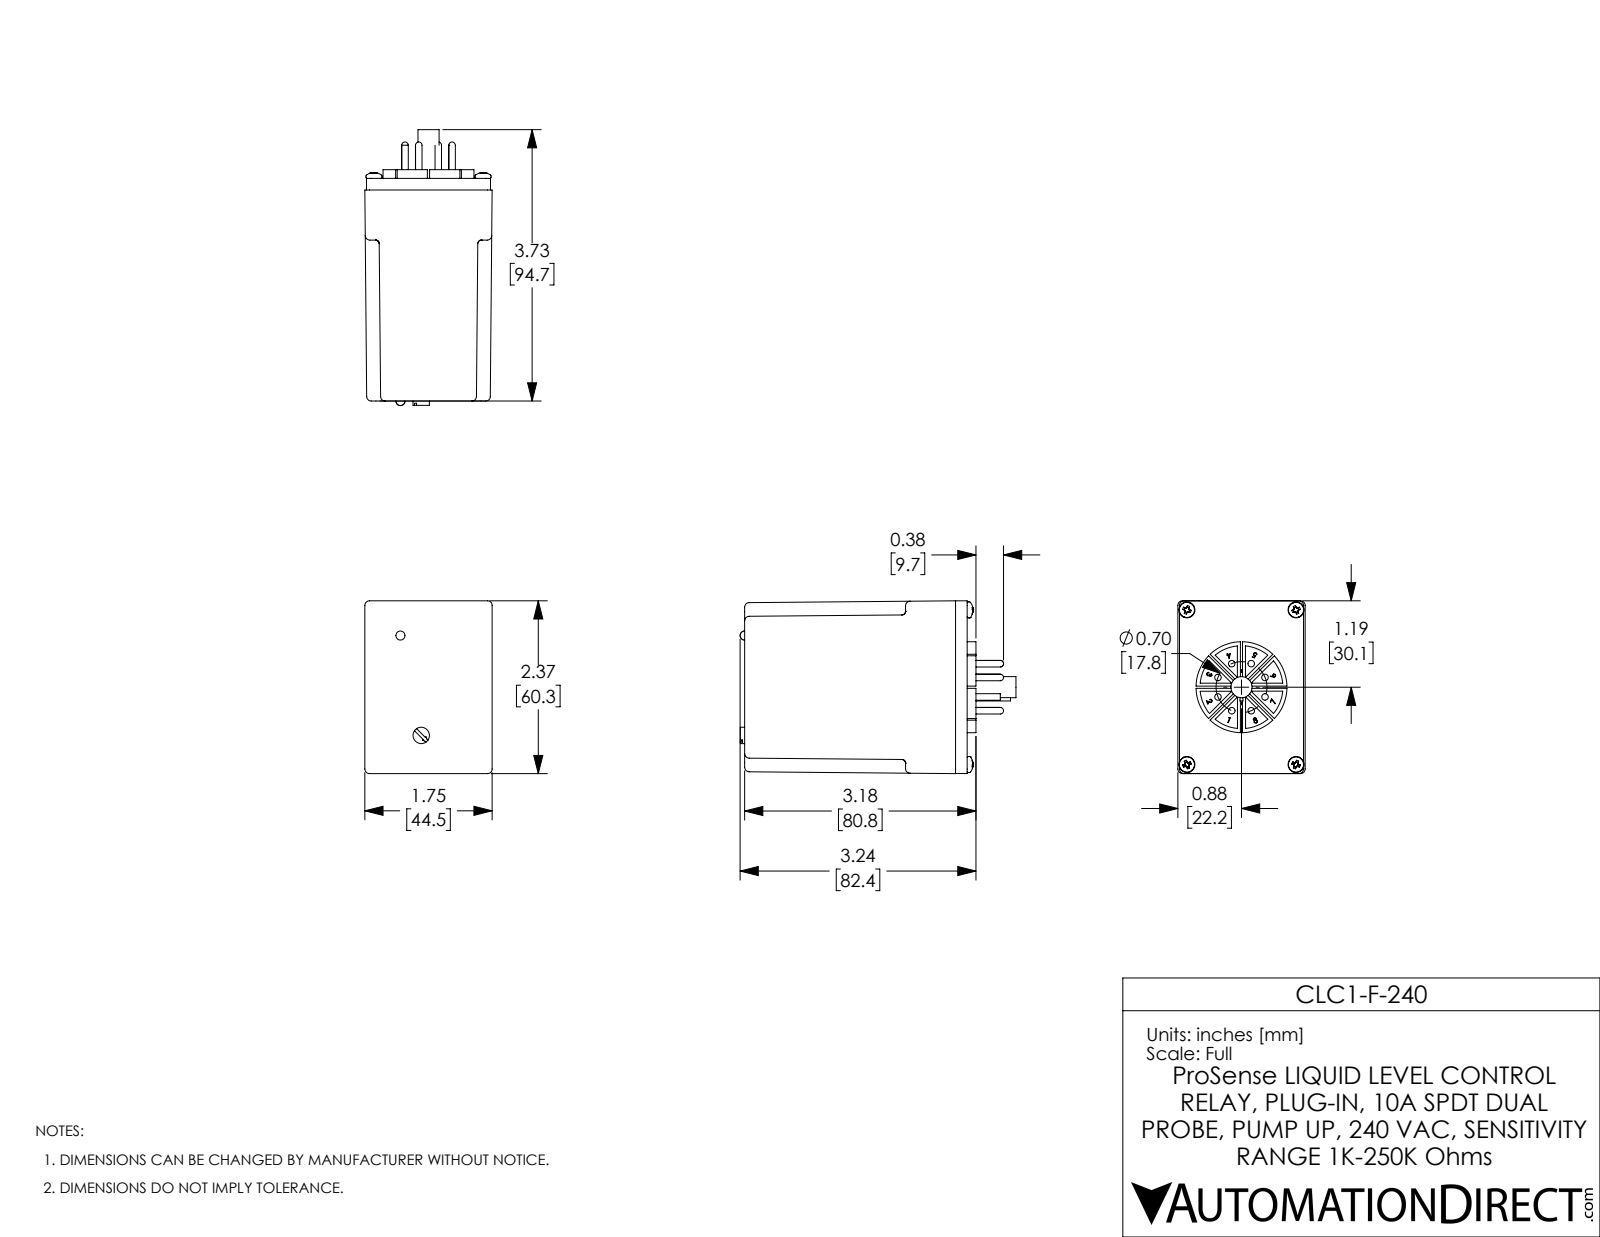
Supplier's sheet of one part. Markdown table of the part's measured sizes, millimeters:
| quantity | value |
| --- | --- |
| part name | CLC1-F-240 |
| STEP written by | SolidWorks 2017 (AUTOMOTIVE_DESIGN) |
| units | millimeters |
| bodies | 16 solids, 706 faces (229 planar, 294 cylindrical, 183 other) |
| overall size | 96.3 × 60.3 × 44.5 |
| volume | 200 600 mm³ |
| surface area | 28 850 mm² |
| round holes (diameter × count) | 3.2 × 4 |
| round bosses / shafts (diameter × count) | 2.3 × 8, 5.6 × 4, 2.8 × 4, 2 × 4, 31.8 × 1, 7.4 × 1, 5.7 × 1 |
| partial cylindrical surfaces (radius × count) | 1.6 × 32, 0.1 × 8, 1.3 × 4, 14.5 × 1 |
| main face-to-face distances | 73.7, 4.1, 77.7, 1.8, 5.8, 79.5, 4.8, 0.8, 80.8, 1.3 |
| hole center spacings | 38.1, 54, 66.1 |
